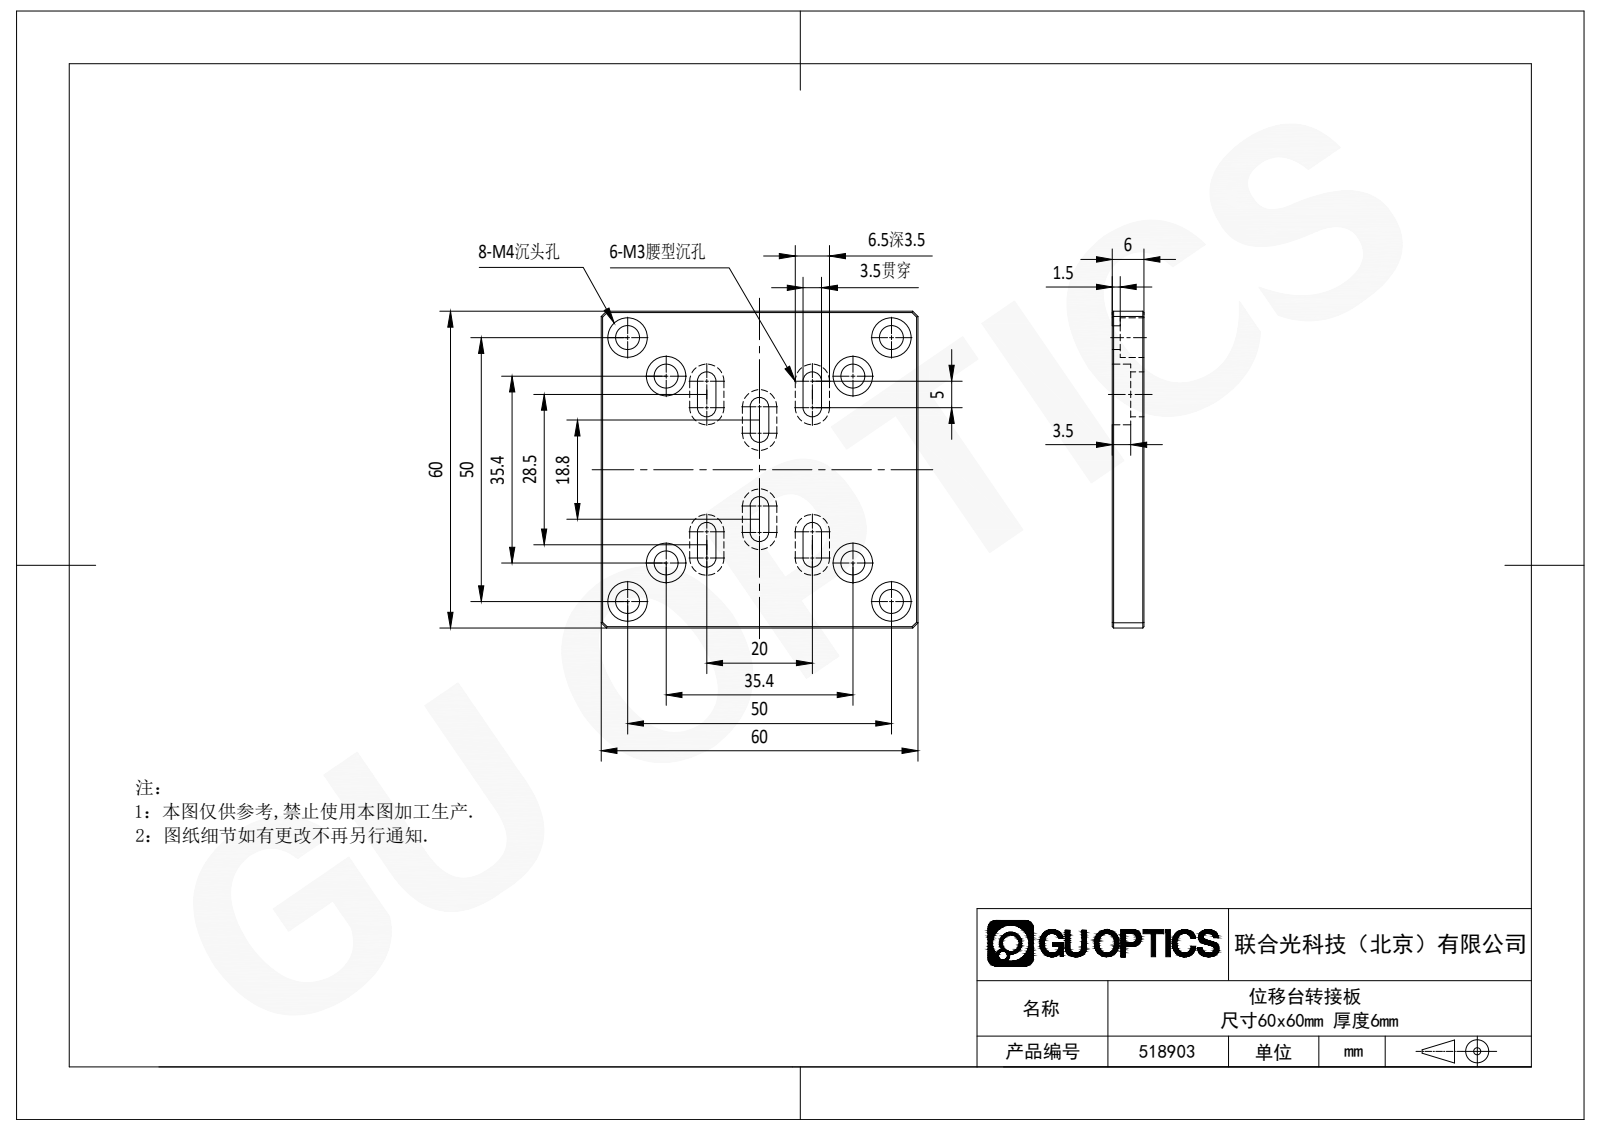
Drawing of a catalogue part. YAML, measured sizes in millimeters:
step_written_by: "SolidWorks 2020 (CONFIG_CONTROL_DESIGN)"
units: millimeters
bodies: {solids: 1, faces: 104, planar: 64, cylindrical: 40, other: 0}
overall_size: [60, 60, 6]
volume: 18237
surface_area: 9887
round_holes:
  - {diameter: 4.5, count: 8}
  - {diameter: 7.5, count: 8}
partial_cylinders:
  - {radius: 1.75, count: 12}
  - {radius: 3.25, count: 12}
face_to_face_distances: [6, 60, 3.5, 1.5, 5, 10, 2.5, 1, 4.5, 15]
hole_center_spacings: [43.32, 10.32, 35.4, 50, 60.39, 50.06, 70.71]
